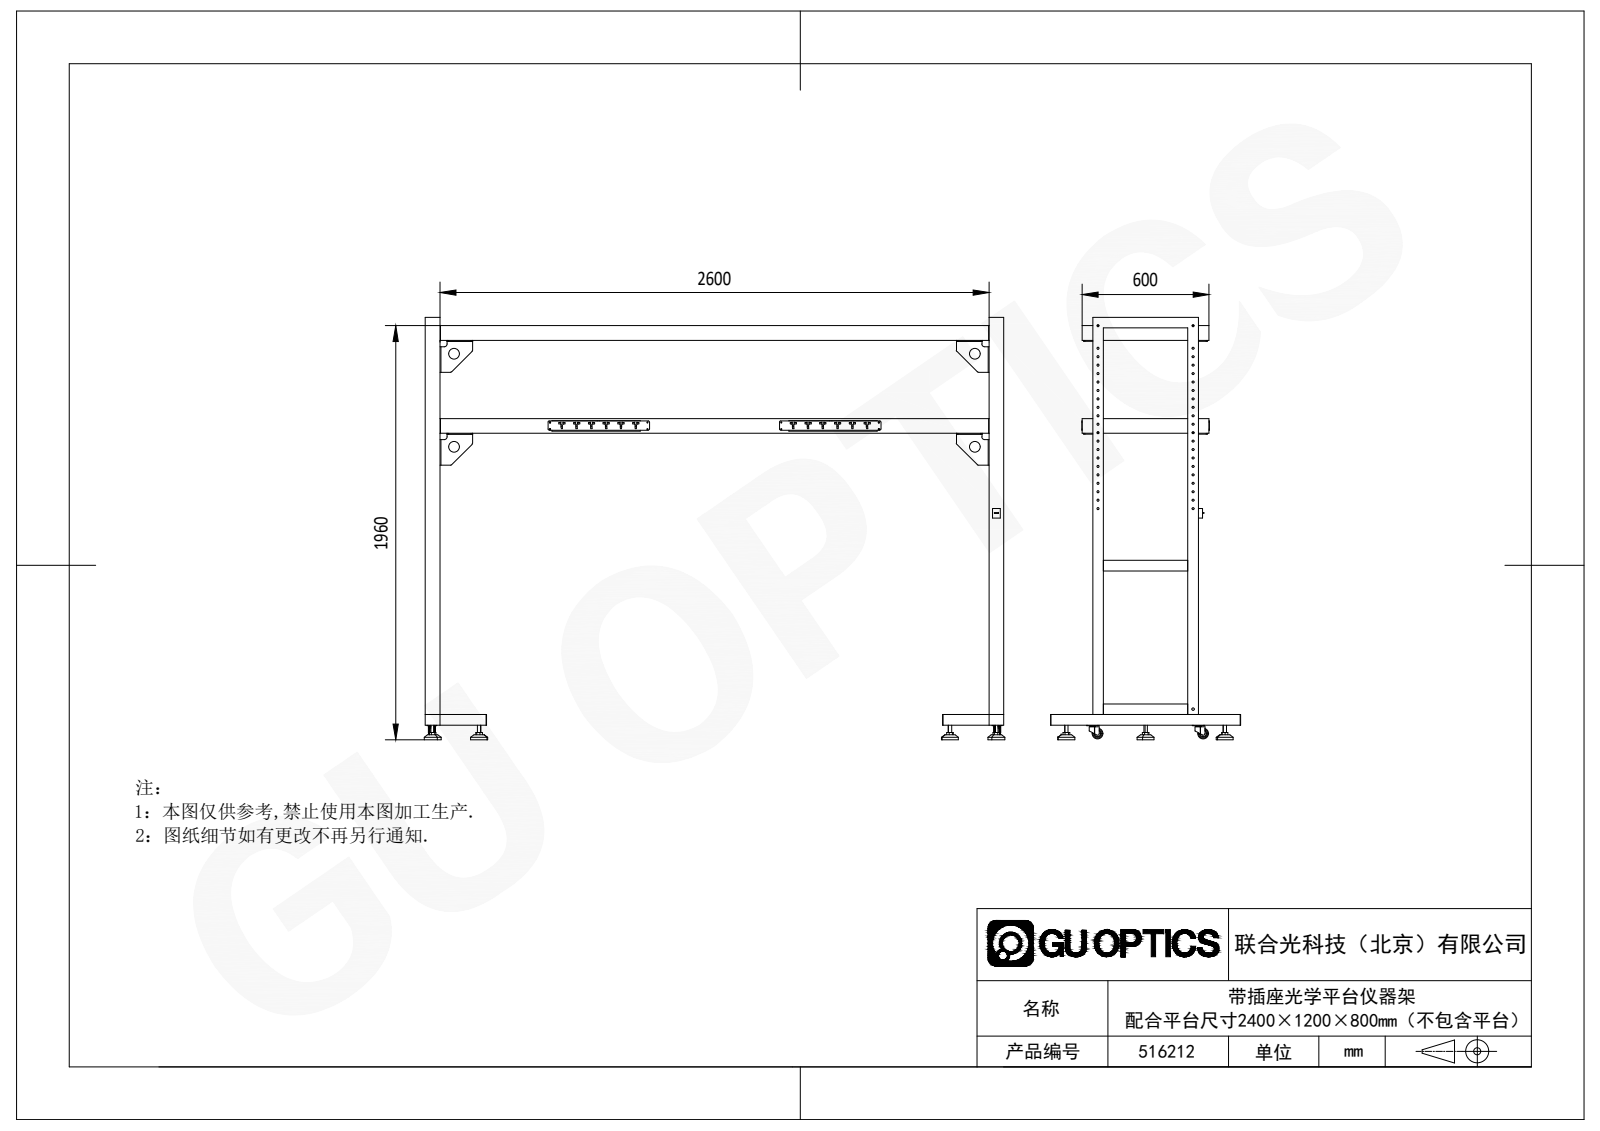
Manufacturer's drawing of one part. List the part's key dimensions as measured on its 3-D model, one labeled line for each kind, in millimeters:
Part name (STEP PRODUCT): 516212
STEP written by: SolidWorks 2020 (CONFIG_CONTROL_DESIGN)
Units: millimetres
Bodies: 57 solids, 2555 faces (1431 planar, 1048 cylindrical, 76 other)
Overall size (bounding box): 2750 × 2001 × 900
Volume: 25 340 000 mm³ · Surface area: 18 180 000 mm²
Round holes (diameter × count): ⌀9 ×66, ⌀6.1 ×16, ⌀10 ×16, ⌀6.5 ×12, ⌀4.2 ×8, ⌀6 ×8, ⌀17 ×6, ⌀18 ×6, ⌀26 ×6, ⌀69 ×6, ⌀3.2 ×4, ⌀5.2 ×4
Round bosses / shafts (diameter × count): ⌀80 ×6, ⌀16 ×6, ⌀26 ×4, ⌀18 ×4, ⌀50 ×2, ⌀10 ×2
Partial cylindrical surfaces — rounded edges, fillets, slot ends (radius × count): R5 ×32, R7 ×24, R3 ×16, R4.25 ×12, R1.5 ×8, R1.51 ×8, R4.01 ×8, R13 ×4
Main face-to-face distances: 440, 1.5, 3, 70, 67, 2, 50, 2.5, 438.5, 67.5
Hole centre spacings: 40, 80, 120, 280, 160, 200, 240, 320
